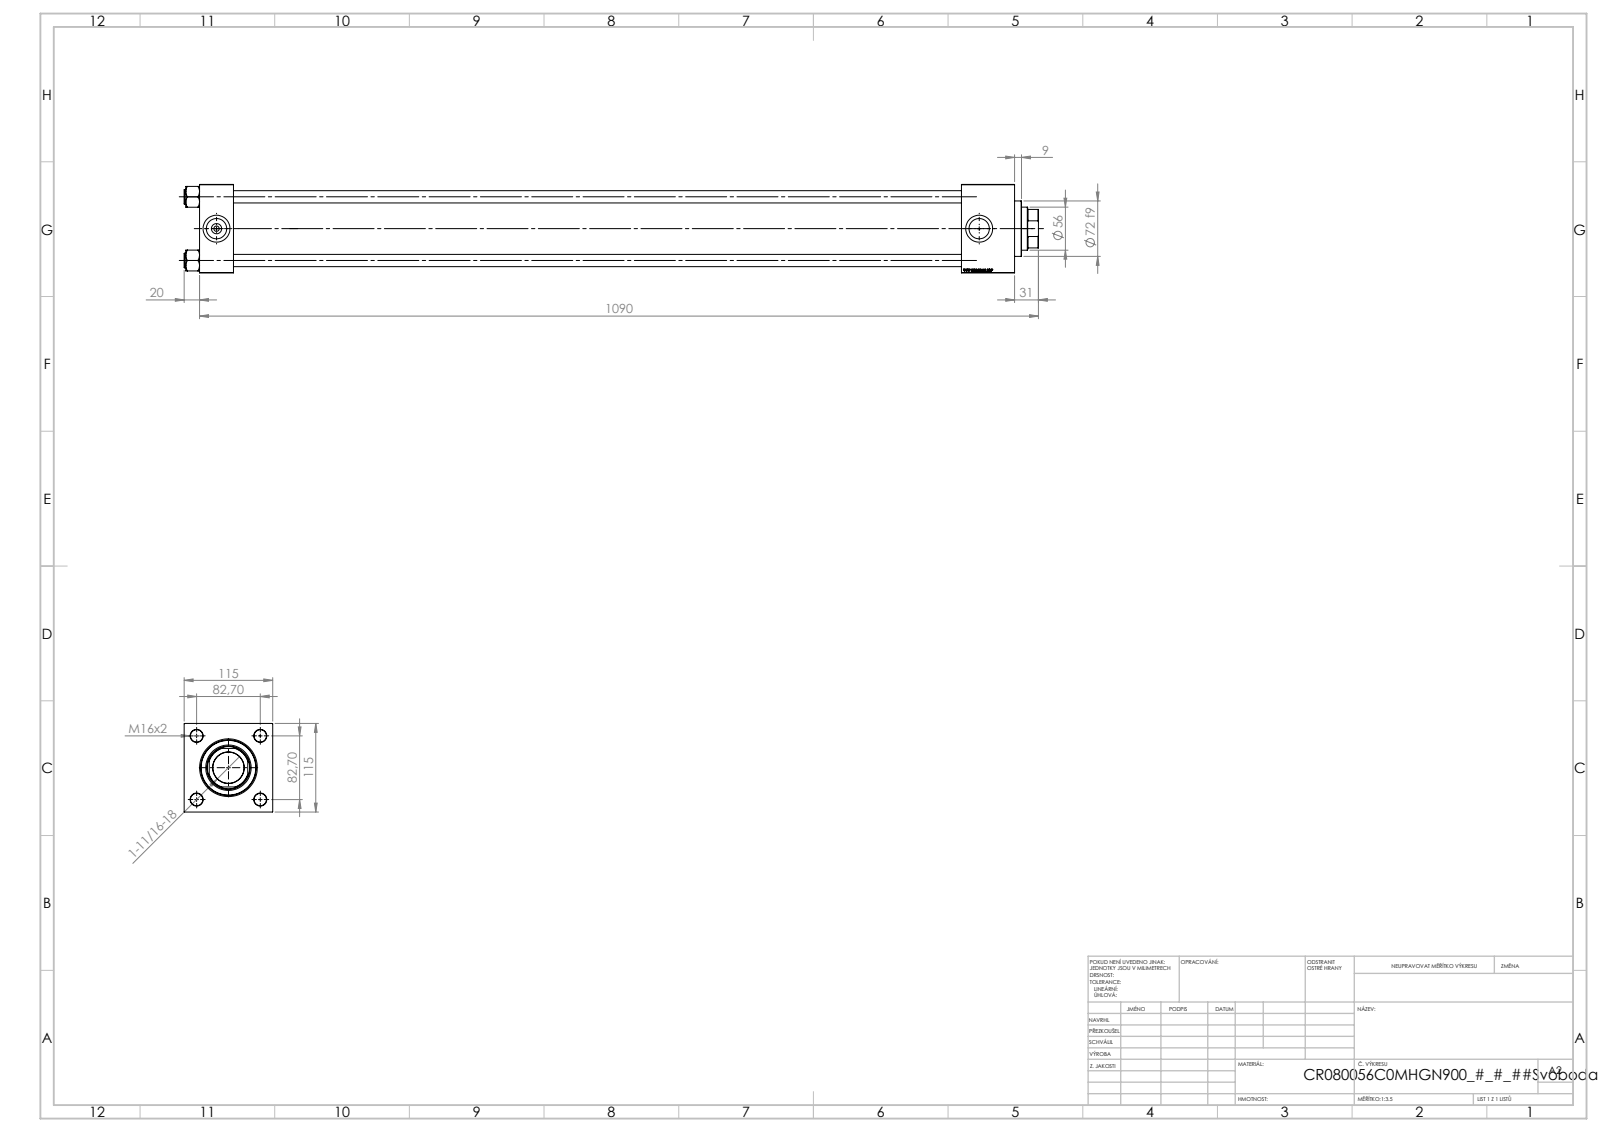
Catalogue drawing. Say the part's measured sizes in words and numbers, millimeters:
The part is named "NUT_M5_C; V215CR_VCP_C; V215_VC_A; V215CR_C_TYCINKA (+1 more)". Its 3-D file was written by "SolidWorks 2019 (CONFIG_CONTROL_DESIGN)". It is 11 solids with 1193 faces: 573 planar, 84 cylindrical and 536 other. Overall it measures 1110 by 115 by 115 millimeters. Its volume is 5 426 000 cubic millimeters and its surface area 1 071 000 square millimeters. Round holes: 4 of diameter 16, 2 of diameter 7, 2 of diameter 26.44, 2 of diameter 35, 1 of diameter 40.5, 1 of diameter 56, 1 of diameter 59, 1 of diameter 61, 1 of diameter 72, 1 of diameter 80. Round bosses or shafts: 4 of diameter 19, 1 of diameter 86. Partial cylindrical surfaces (rounded edges, fillets, slot ends): 1 of radius 27. The main face-to-face distances are 115, 44, 990, 946, 1059, 1015, 69, 1030.3, 986.3, 40.3. The hole center spacings are 58.48, 82.7, 116.96, 991.
